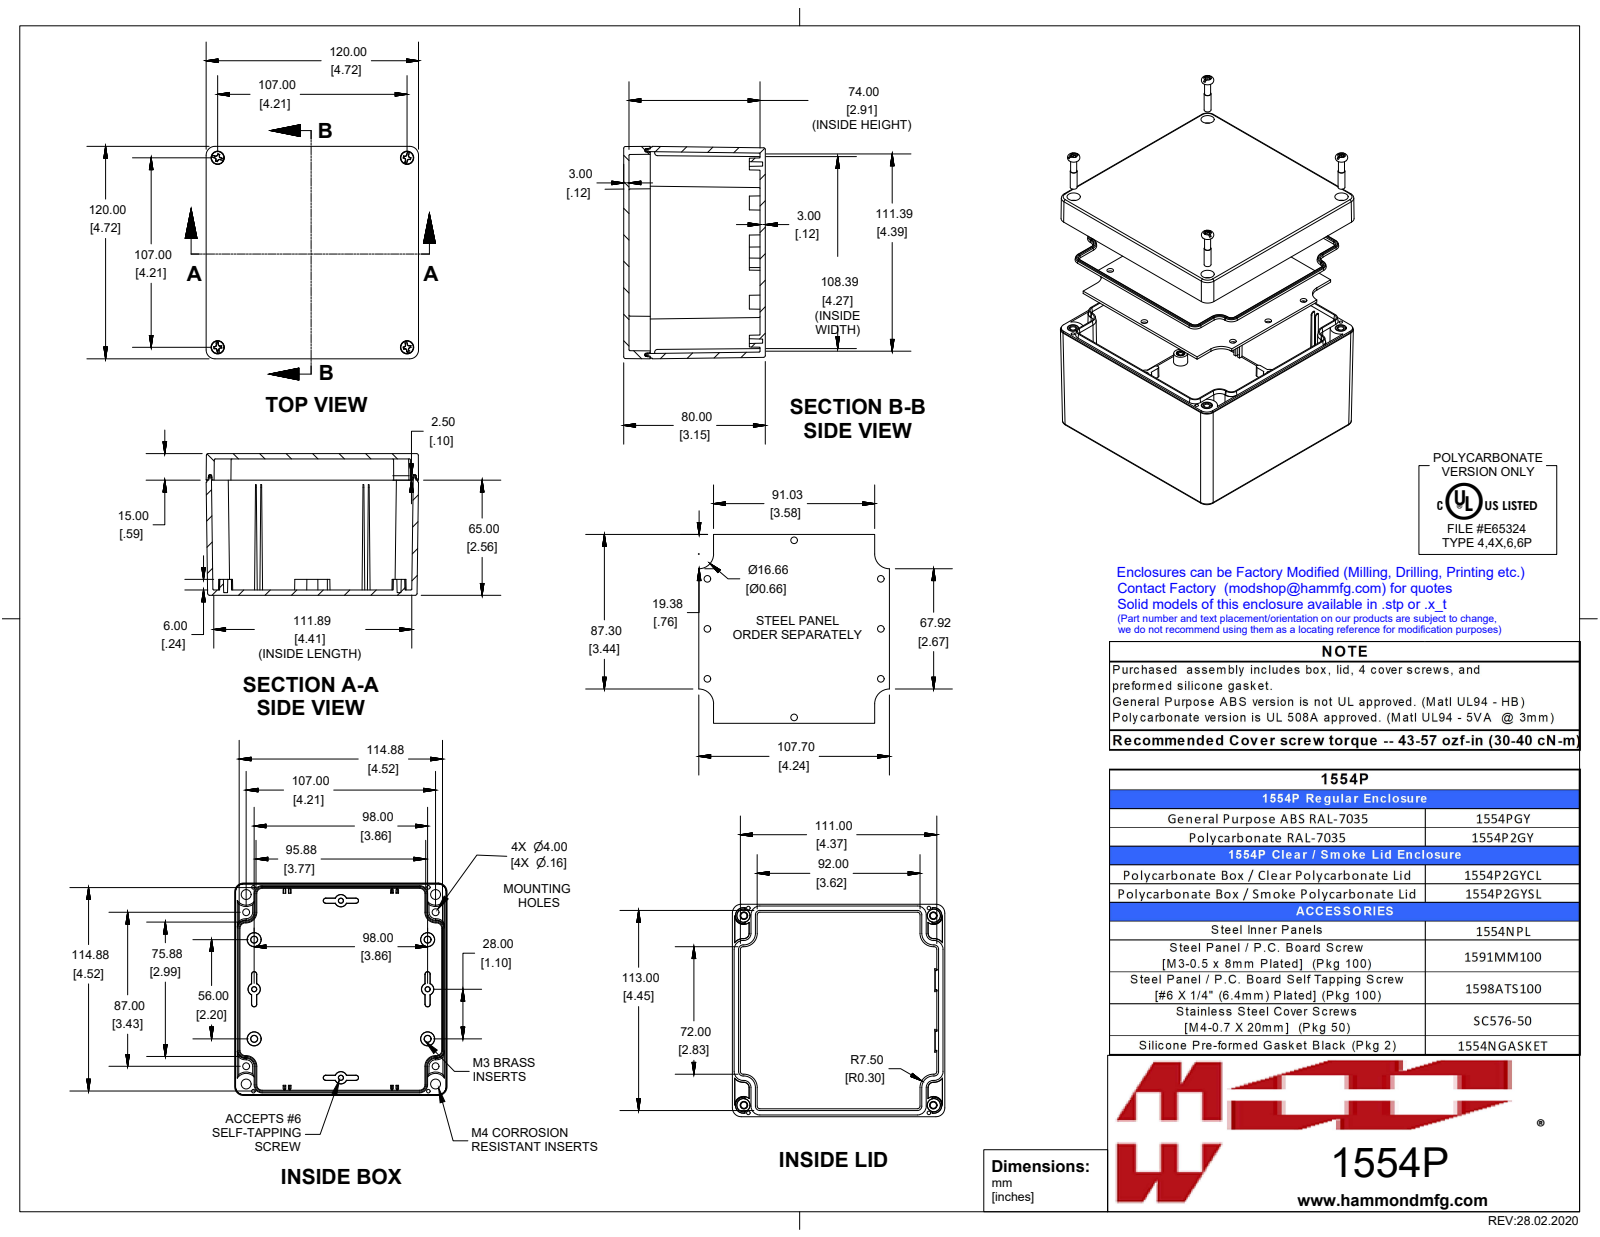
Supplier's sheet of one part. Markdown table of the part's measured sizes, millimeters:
| quantity | value |
| --- | --- |
| part name | 1554PGY |
| STEP written by | SolidWorks 2019 (AUTOMOTIVE_DESIGN) |
| units | millimeters |
| bodies | 16 solids, 1384 faces (394 planar, 346 cylindrical, 644 other) |
| overall size | 120 × 120 × 80 |
| volume | 236 800 mm³ |
| surface area | 180 600 mm² |
| round holes (diameter × count) | 2 × 8, 2.5 × 4, 2.8 × 4, 3.3 × 4, 3.5 × 4, 3.7 × 4 |
| round bosses / shafts (diameter × count) | 6.4 × 4, 5.5 × 4, 5.3 × 4, 4.8 × 4, 3.9 × 4, 3.9 × 4, 3.8 × 4, 3.4 × 4 |
| partial cylindrical surfaces (radius × count) | 0.5 × 52, 1 × 8, 5 × 8, 8.3 × 4, 1.5 × 2 |
| main face-to-face distances | 3, 77, 80, 9, 68, 74, 6, 71, 10.6, 7.6 |
| hole center spacings | 98, 53.6, 5, 25.9, 28, 29.3, 29.9, 51.6 |
